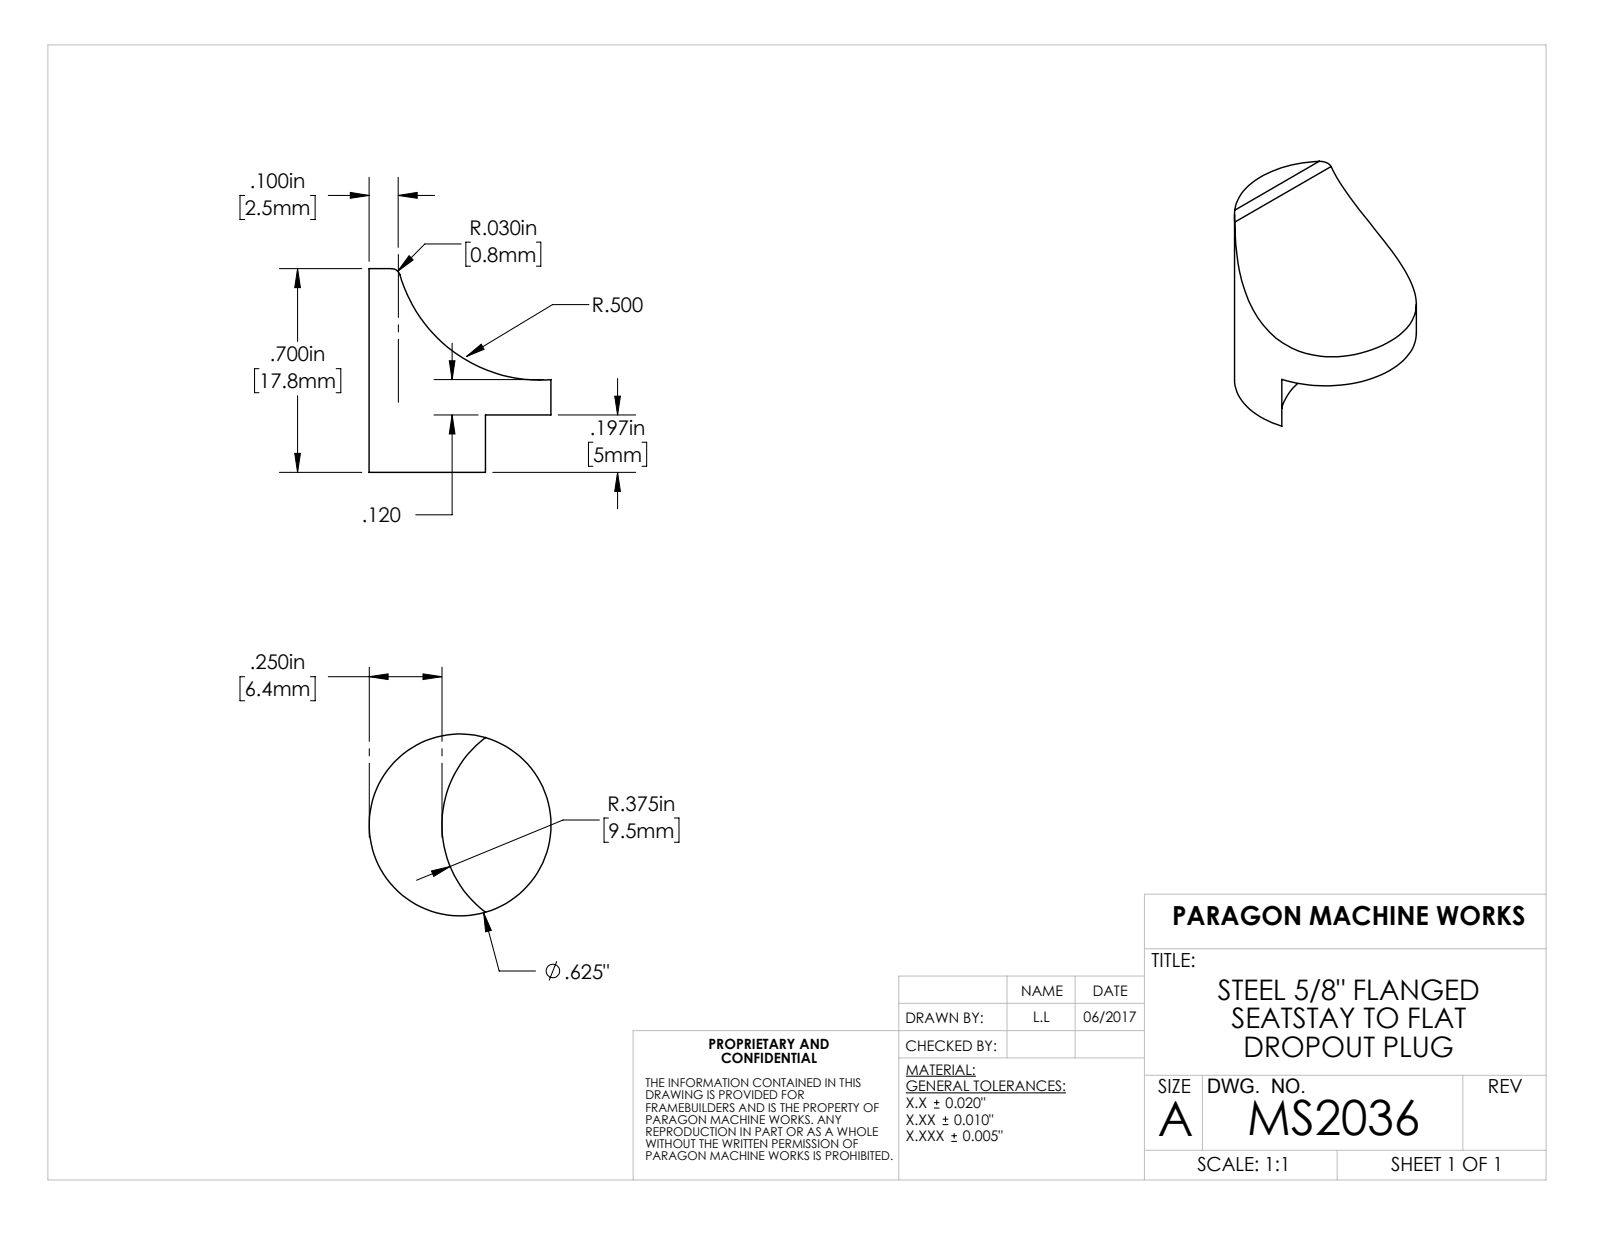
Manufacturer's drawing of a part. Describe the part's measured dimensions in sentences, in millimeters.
The part is named "MS2036". Its 3-D file was written by "SolidWorks 2017 (AUTOMOTIVE_DESIGN)". It is 1 solid with 8 faces: 3 planar, 5 cylindrical and 0 other. Overall it measures 17.8 by 15.9 by 15.9 millimeters. Its volume is 1 700 cubic millimeters and its surface area 1 041 square millimeters. Round bosses or shafts: 1 of diameter 15.9. Partial cylindrical surfaces (rounded edges, fillets, slot ends): 1 of radius 0.8, 1 of radius 9.5, 1 of radius 12.7. The main face-to-face distances are 5, 17.8, 12.8.
